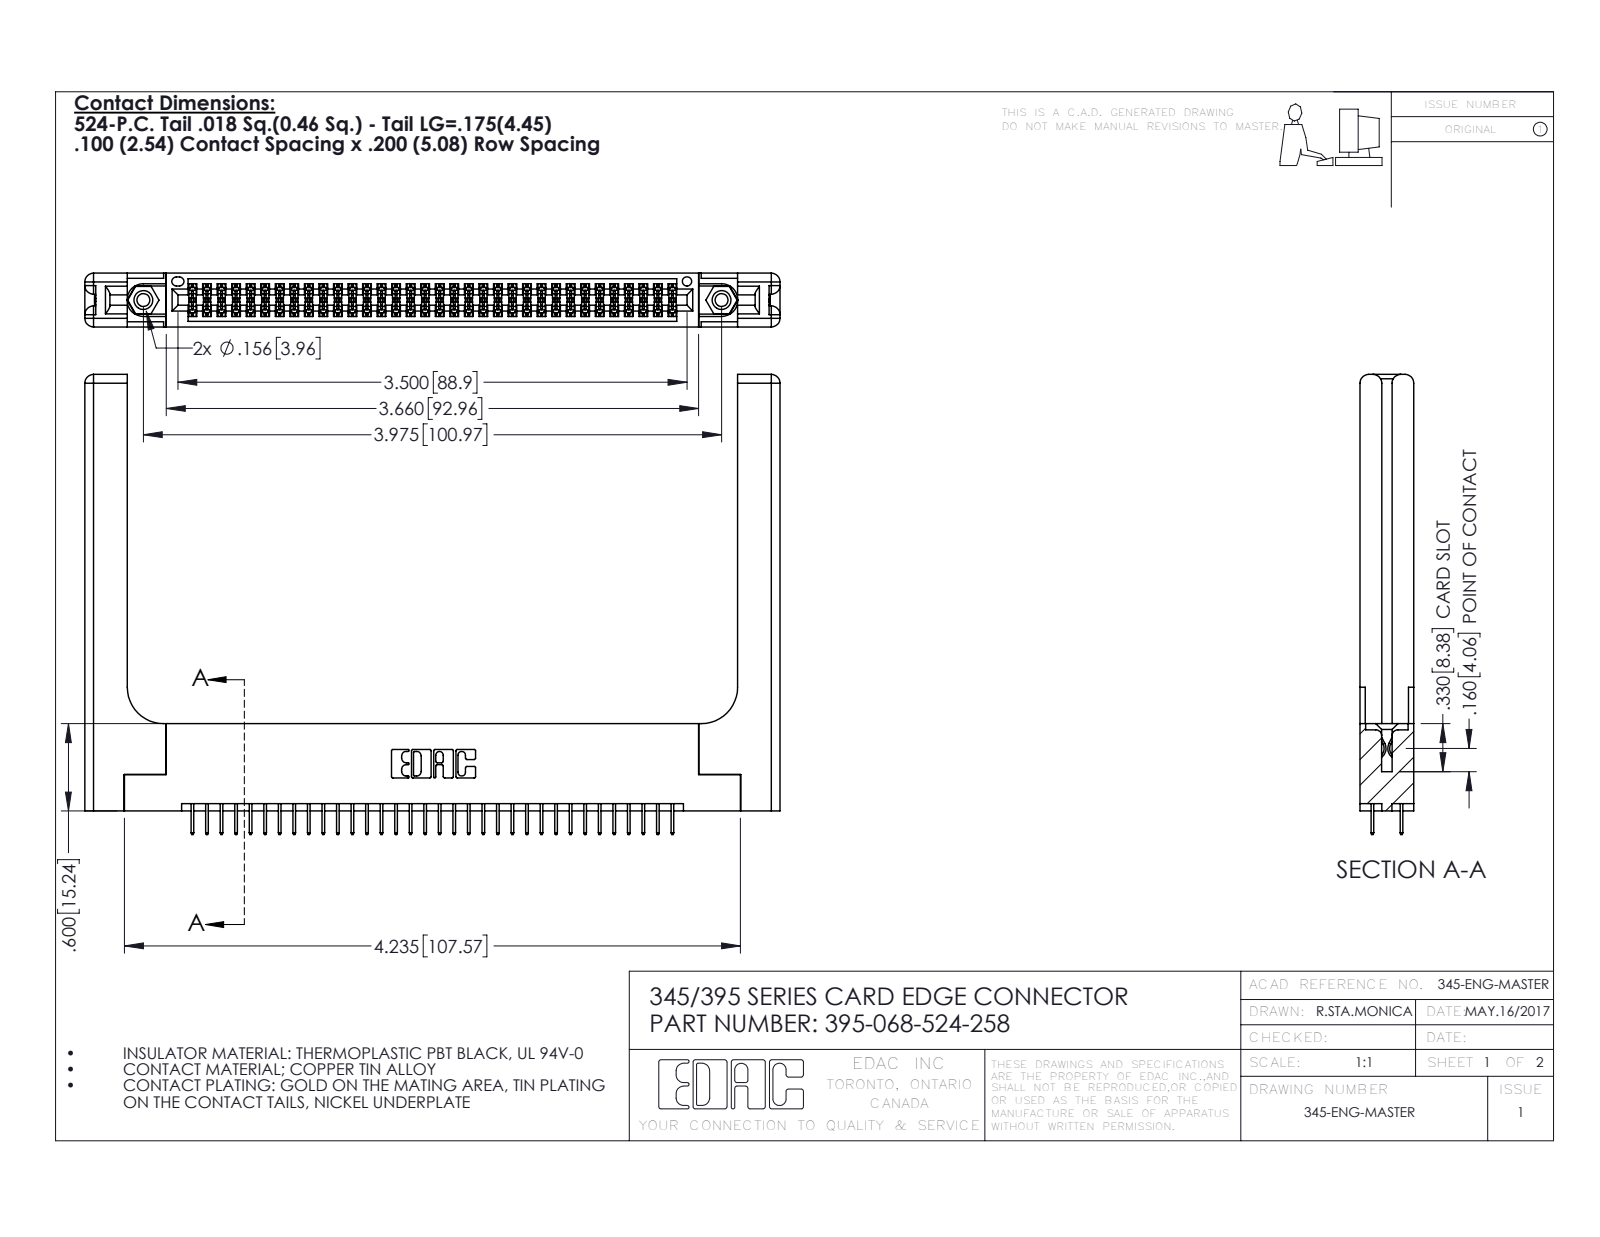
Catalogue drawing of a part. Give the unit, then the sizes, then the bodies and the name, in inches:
Units: inches
Overall size (bounding box): 4.779 × 3.162 × 0.37
Round holes (diameter × count): ⌀0.089 ×2, ⌀0.125 ×2, ⌀0.156 ×2, ⌀0.064 ×1
Round bosses / shafts (diameter × count): ⌀0.155 ×2
Partial cylindrical surfaces — rounded edges, fillets, slot ends (radius × count): R0.006 ×102, R0.01 ×22, R0.06 ×16, R0.007 ×6, R0.031 ×6, R0.026 ×3, R0.014 ×2, R0.019 ×2
Main face-to-face distances: 0.37, 0.072, 0.298, 0.2, 0.098, 0.272, 0.025, 0.225, 0.148, 0.15
Hole centre spacings: 0.27, 3.74, 3.975
Volume: 1.226 in³ · Surface area: 33.79 in²
Bodies: 73 solids, 4054 faces (2880 planar, 1114 cylindrical, 60 other)
Part name (STEP PRODUCT): 345 Part_Flush Mounting Lugs - 0.156 Dia-TH; 345-250-001_345-250-001-102; 395-068-524-258; 345-220-058_345-220-058 (+1 more)
STEP written by: SolidWorks 2016 (CONFIG_CONTROL_DESIGN)
